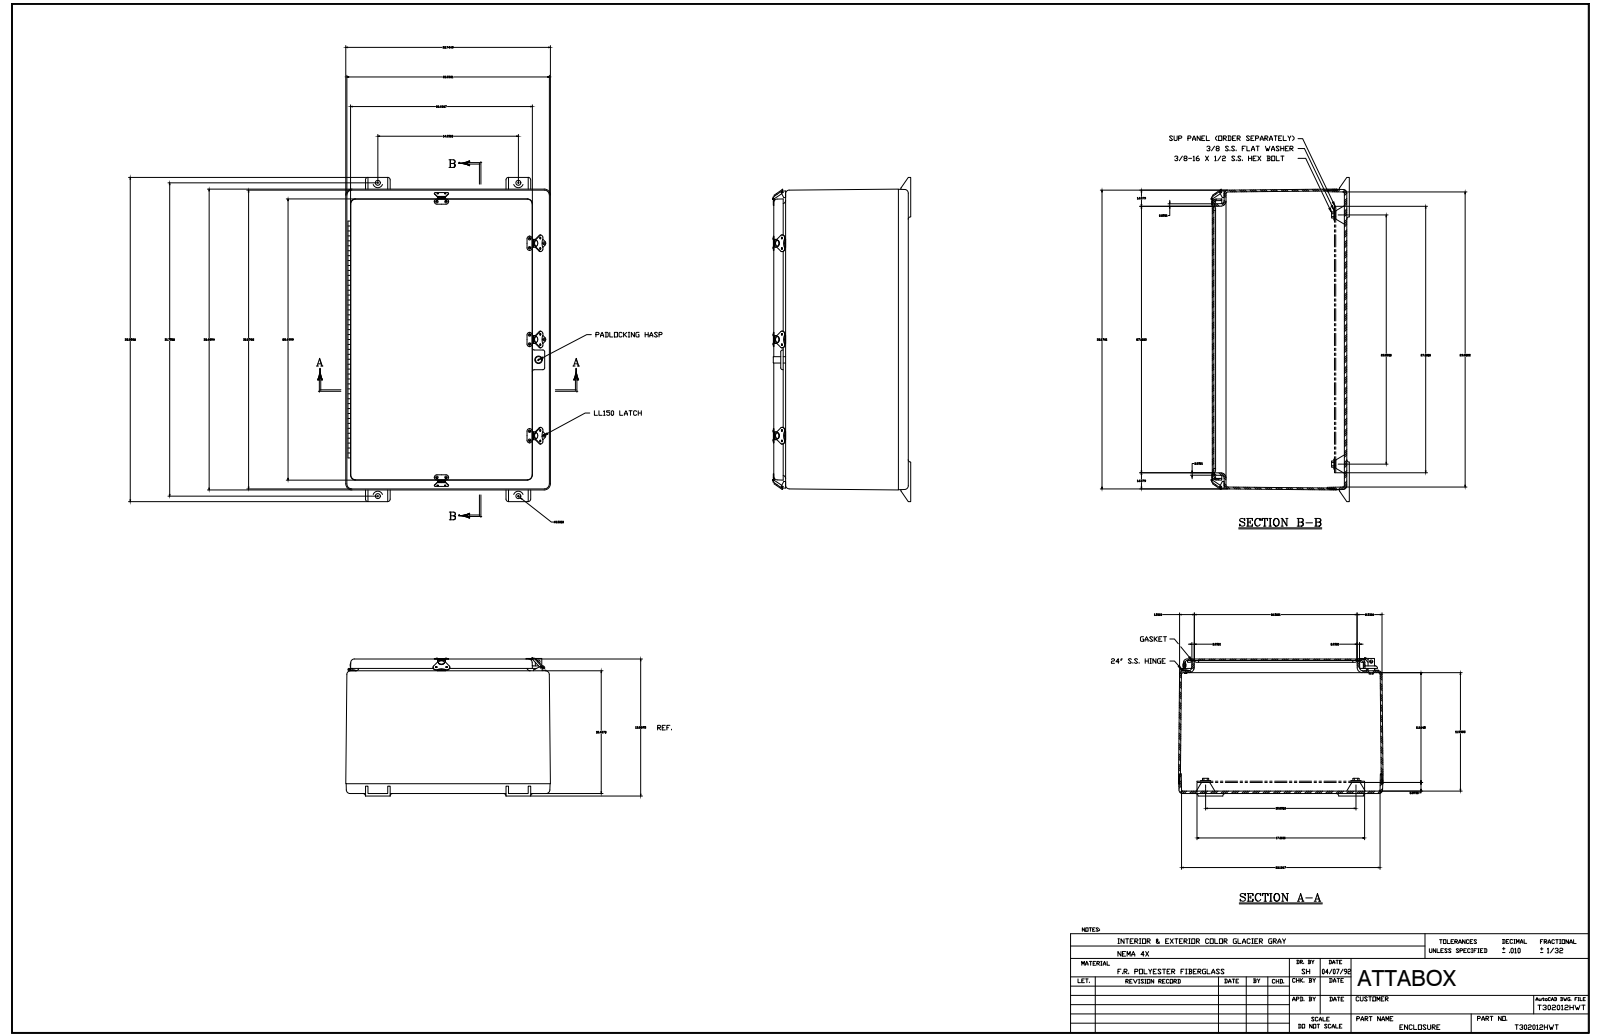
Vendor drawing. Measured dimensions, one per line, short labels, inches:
name: T302012HWT
written by: SolidWorks 2018 (AUTOMOTIVE_DESIGN)
unit: in
bodies: 63 solids, 1720 faces (656 planar, 698 cylindrical, 366 other)
size: 32.844 × 20.75 × 14.241
volume: 560.9 in³; area: 6 021 in²
holes: 36× ⌀0.13, 20× ⌀0.063, 10× ⌀0.138, 10× ⌀0.187, 5× ⌀0.065, 4× ⌀0.563, 3× ⌀0.065, 3× ⌀0.156, 2× ⌀0.135, 2× ⌀0.51, 2× ⌀0.51, 1× ⌀0.125
bosses: 20× ⌀0.14, 8× ⌀0.297, 5× ⌀0.5, 3× ⌀0.2, 2× ⌀0.135, 1× ⌀0.25, 1× ⌀0.201
rounds: 127× R0.01, 21× R0.375, 20× R0.03, 20× R0.25, 18× R0.187, 18× R0.312, 12× R0.5, 11× R0.188
face distances: 0.187, 0.25, 13.219, 13.469, 0.156, 13.375, 13.625, 1.187, 12.437, 12.25
hole spacings: 9.75, 0.858, 1.542, 7.5, 15.5, 19.5, 1, 3.211
